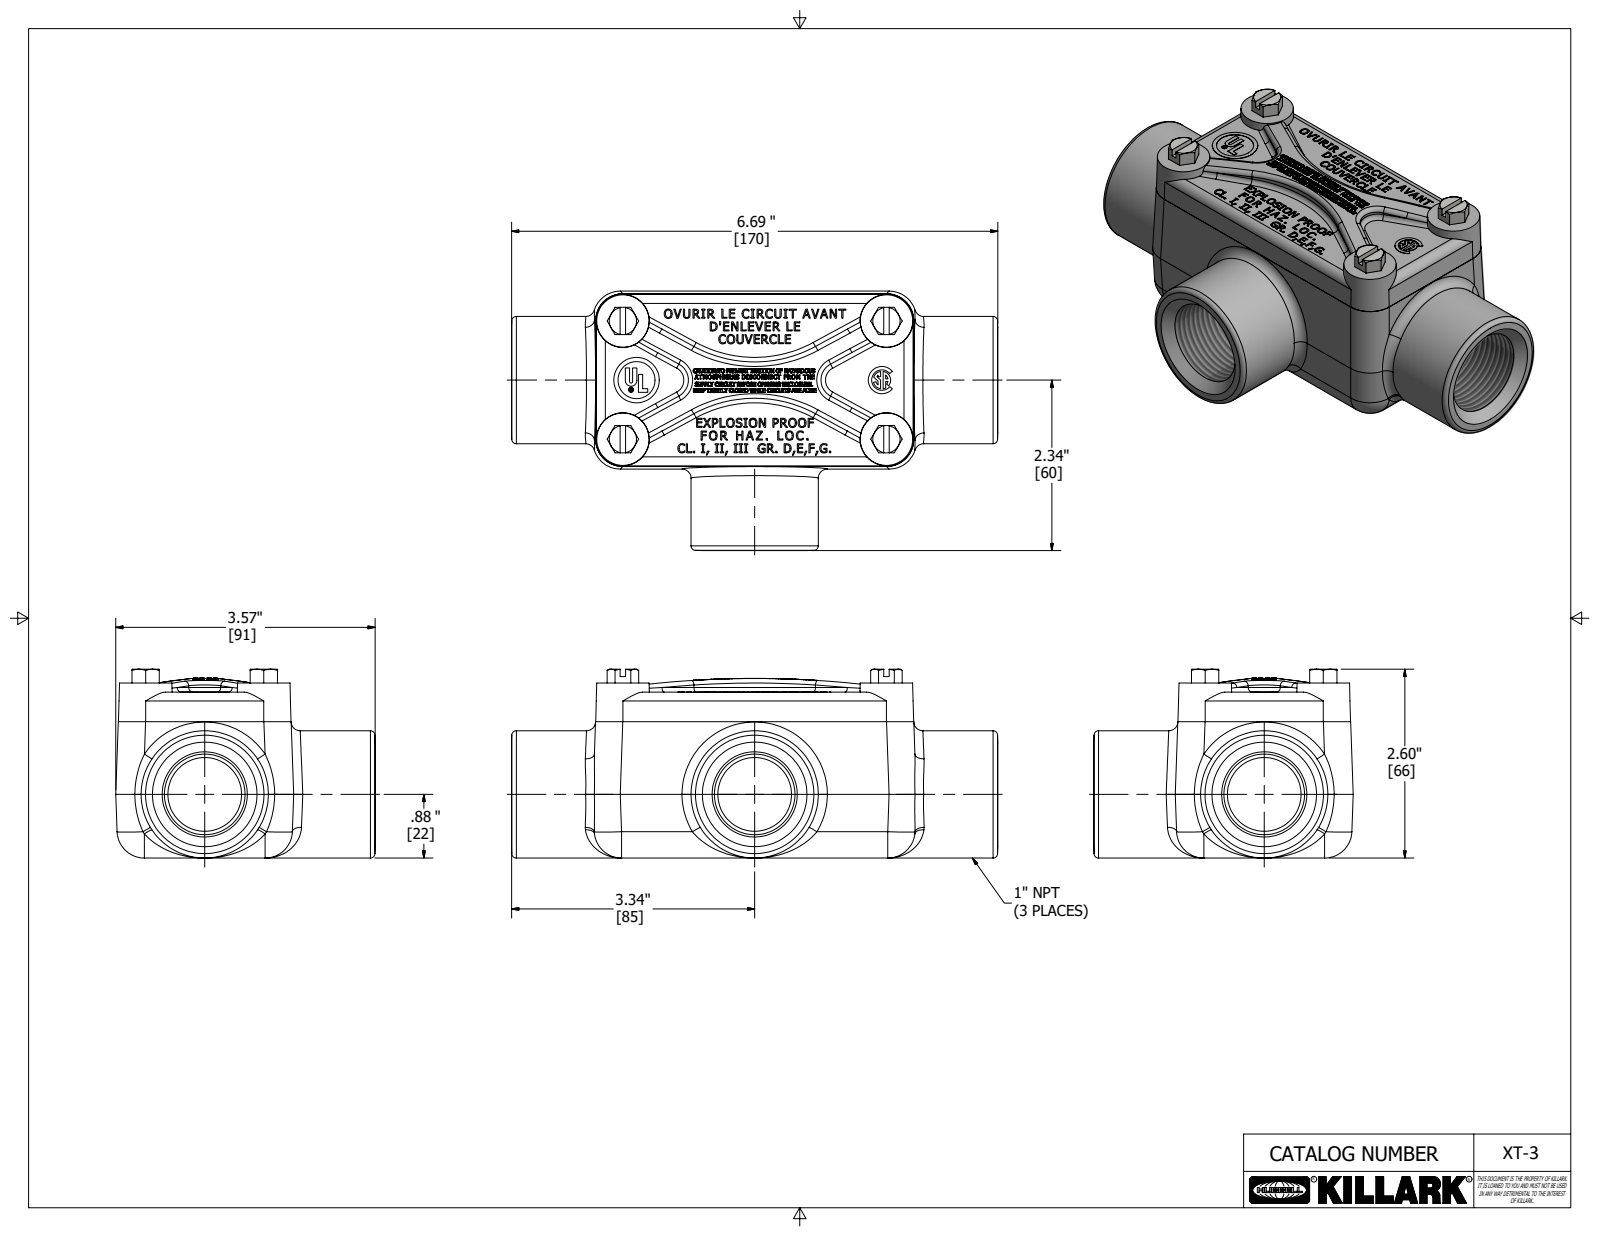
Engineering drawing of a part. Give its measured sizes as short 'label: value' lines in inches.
name: XT-3; 10820-2; 0248904M; 0723660B
written by: Autodesk Inventor 2020 (AUTOMOTIVE_DESIGN)
unit: in
bodies: 6 solids, 5033 faces (2658 planar, 315 cylindrical, 2060 other)
size: 6.688 × 3.567 × 2.596
volume: 15.25 in³; area: 132.4 in²
holes: 4× ⌀0.196, 2× ⌀1.013, 1× ⌀0.058, 1× ⌀0.509
bosses: 4× ⌀0.25, 2× ⌀1.75, 1× ⌀0.625, 1× ⌀0.069
rounds: 34× R0.125, 12× R0.062, 12× R0.375, 5× R0.187, 4× R0.109, 4× R0.313, 2× R0.094, 2× R0.25
face distances: 0.187, 1.687, 2.257, 2.094, 0.406, 1.875, 2.281, 2.07, 2.445, 0.031
hole spacings: 0.834, 1.625, 3.532, 3.625, 3.973, 0.153, 0.689, 0.952
